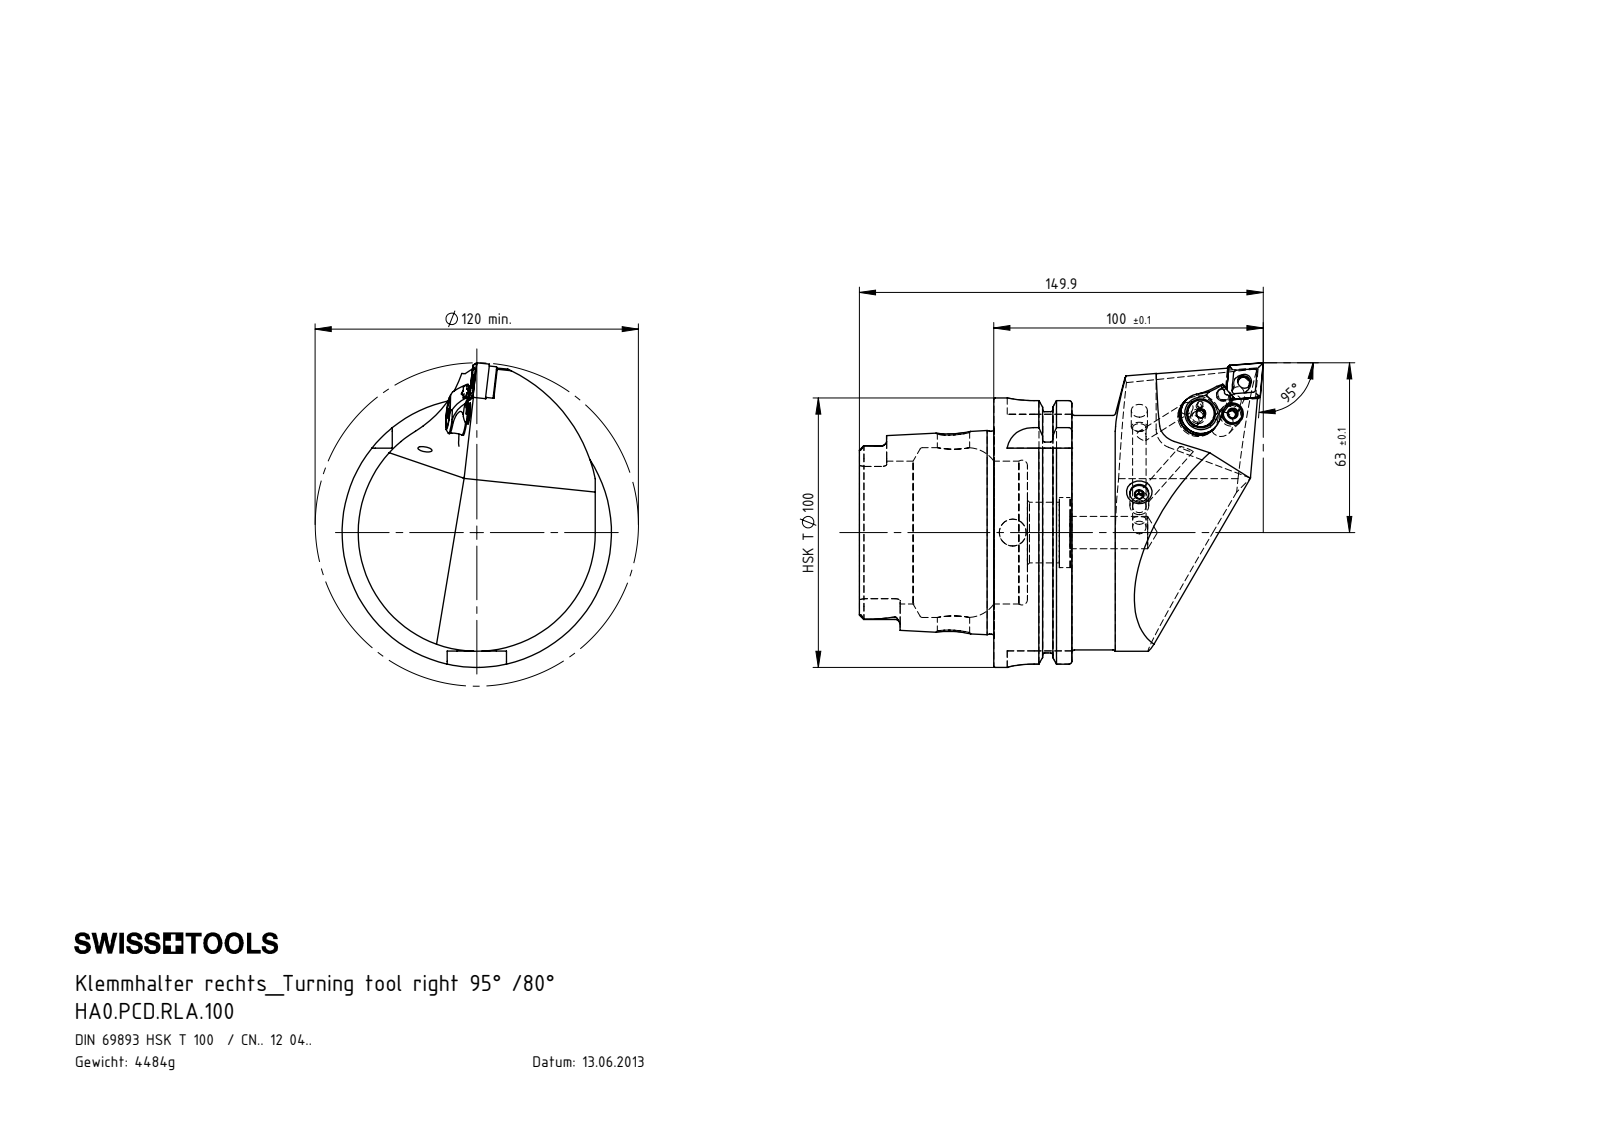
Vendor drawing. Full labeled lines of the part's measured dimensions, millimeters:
Part name (STEP PRODUCT): WCD-ER3.101.000_A; WCD-ER4.101.017_A; WCD-ER2.101.003_A; CNMG120404 (+3 more)
STEP written by: SolidWorks 2012 (CONFIG_CONTROL_DESIGN)
Units: millimetres
Bodies: 7 solids, 368 faces (113 planar, 105 cylindrical, 150 other)
Overall size (bounding box): 149.9 × 113 × 100
Volume: 557 460 mm³ · Surface area: 71 800 mm²
Round holes (diameter × count): ⌀5 ×3, ⌀12 ×2, ⌀5.16 ×1, ⌀6 ×1, ⌀6.4 ×1, ⌀7 ×1, ⌀8.4 ×1, ⌀10 ×1, ⌀22.5 ×1, ⌀26 ×1, ⌀53 ×1, ⌀63 ×1
Round bosses / shafts (diameter × count): ⌀100 ×1, ⌀91.95 ×1, ⌀87 ×1, ⌀75.26 ×1, ⌀8 ×1, ⌀7.9 ×1, ⌀6.4 ×1, ⌀6 ×1
Partial cylindrical surfaces — rounded edges, fillets, slot ends (radius × count): R1.9 ×6, R0.4 ×4, R1 ×4, R10 ×4, R2.5 ×2, R4.83 ×2, R4.88 ×2, R2.1 ×1
Main face-to-face distances: 12.45, 28.95, 16.5, 49.9, 62.35, 78.85, 87.8, 78.2, 28.3, 15.85
Hole centre spacings: 12.79, 12.84
